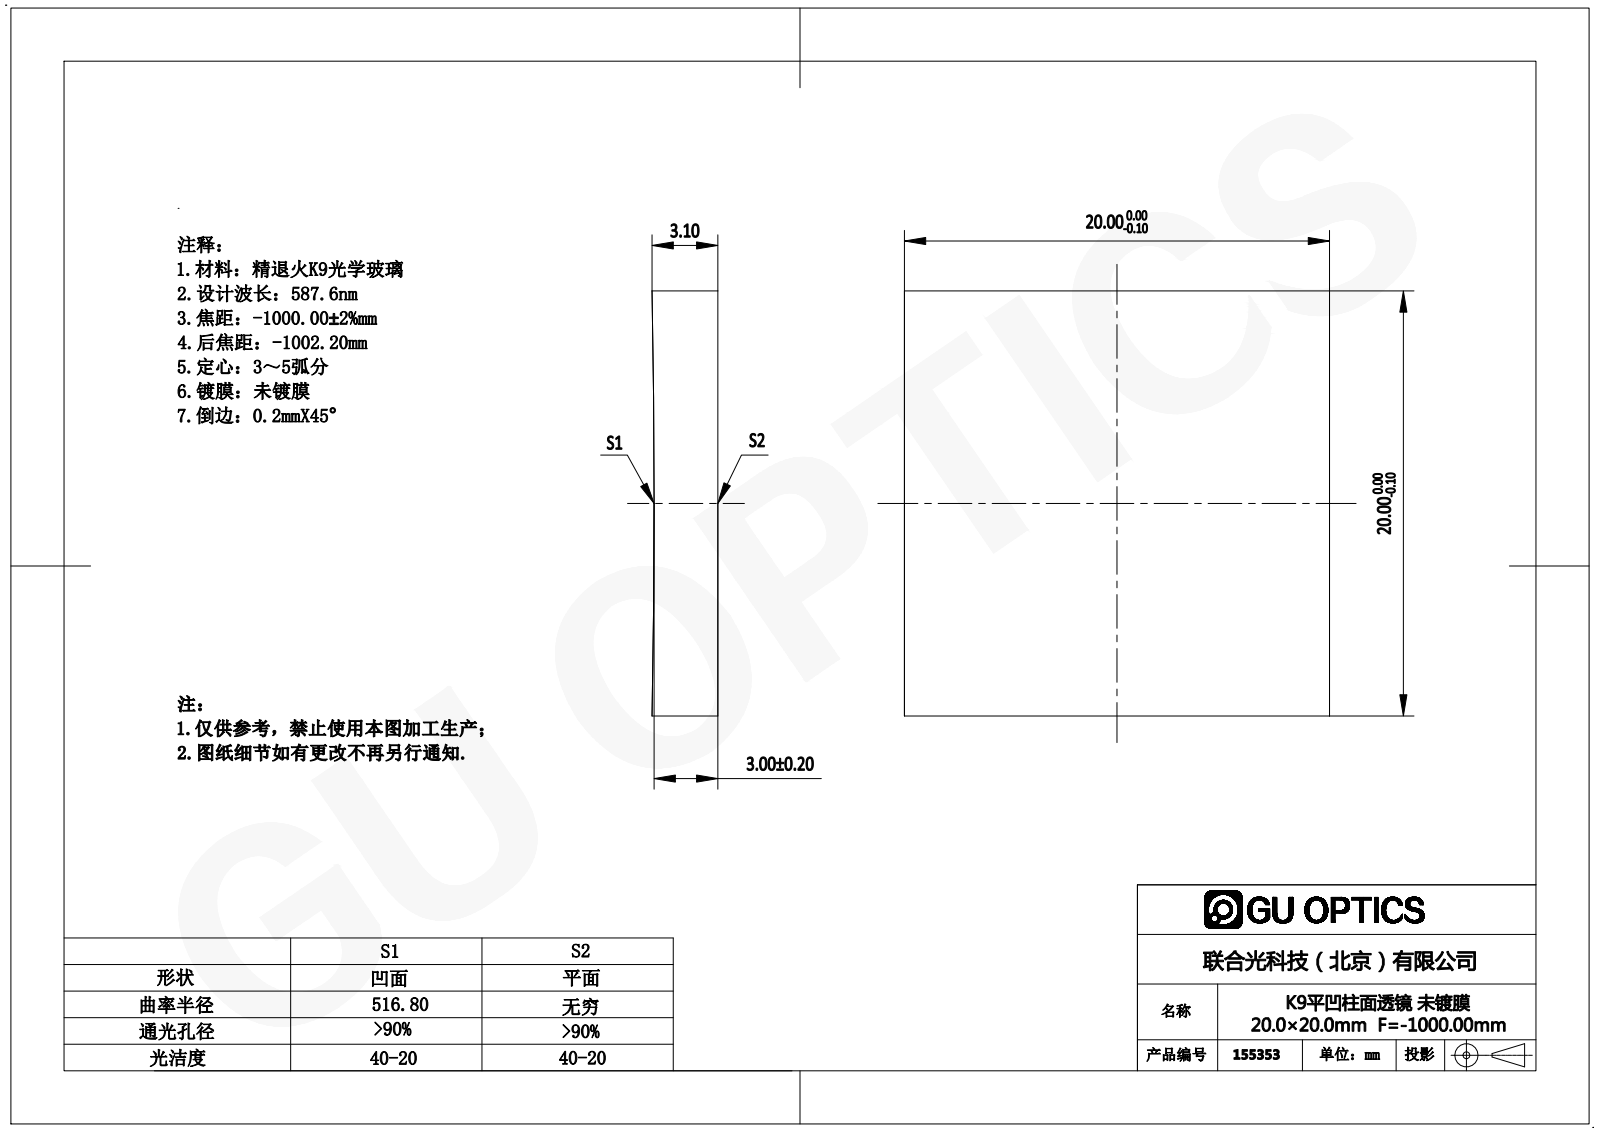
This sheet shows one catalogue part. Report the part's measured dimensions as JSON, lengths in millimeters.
{"part_name": "155353", "step_written_by": "SolidWorks 2016 (AUTOMOTIVE_DESIGN)", "units": "millimeters", "bodies": {"solids": 1, "faces": 6, "planar": 5, "cylindrical": 1, "other": 0}, "overall_size": [20, 20, 3.1], "volume_mm3": 1213, "surface_area_mm2": 1045, "partial_cylinders_radius": [[516.8, 1]], "face_to_face_distances": [20]}
